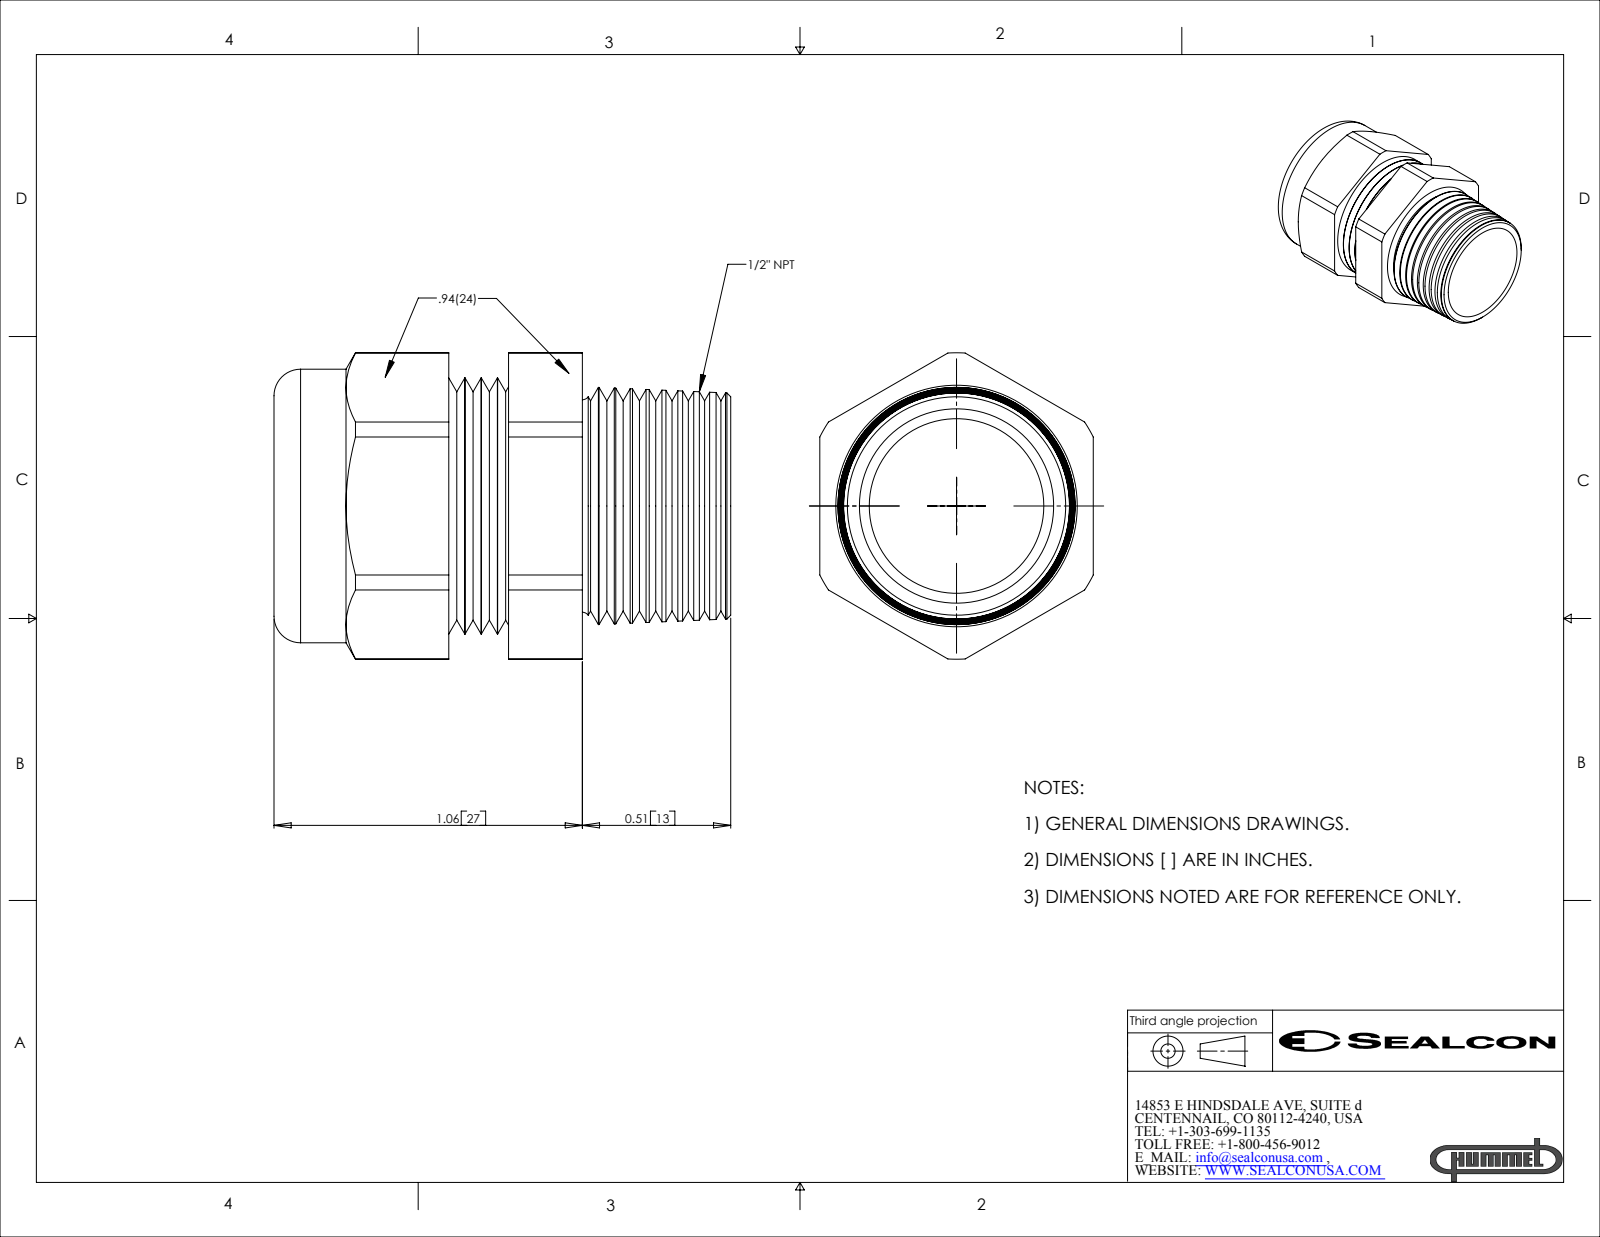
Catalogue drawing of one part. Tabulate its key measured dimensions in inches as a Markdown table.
| quantity | value |
| --- | --- |
| part name | CD13NA-BK |
| STEP written by | SolidWorks 2007 (CONFIG_CONTROL_DESIGN) |
| units | inches |
| bodies | 2 solids, 138 faces (20 planar, 30 cylindrical, 88 other) |
| overall size | 1.57 × 1.053 × 0.94 |
| volume | 0.494 in³ |
| surface area | 11.42 in² |
| round holes (diameter × count) | 0.6 × 1, 0.697 × 1 |
| round bosses / shafts (diameter × count) | 0.94 × 1, 0.88 × 1 |
| partial cylindrical surfaces (radius × count) | 0.526 × 1 |
| main face-to-face distances | 0.94, 0.813, 0.559, 0.254, 0.354, 0.206, 0.459, 1.322, 0.969, 0.763 |
